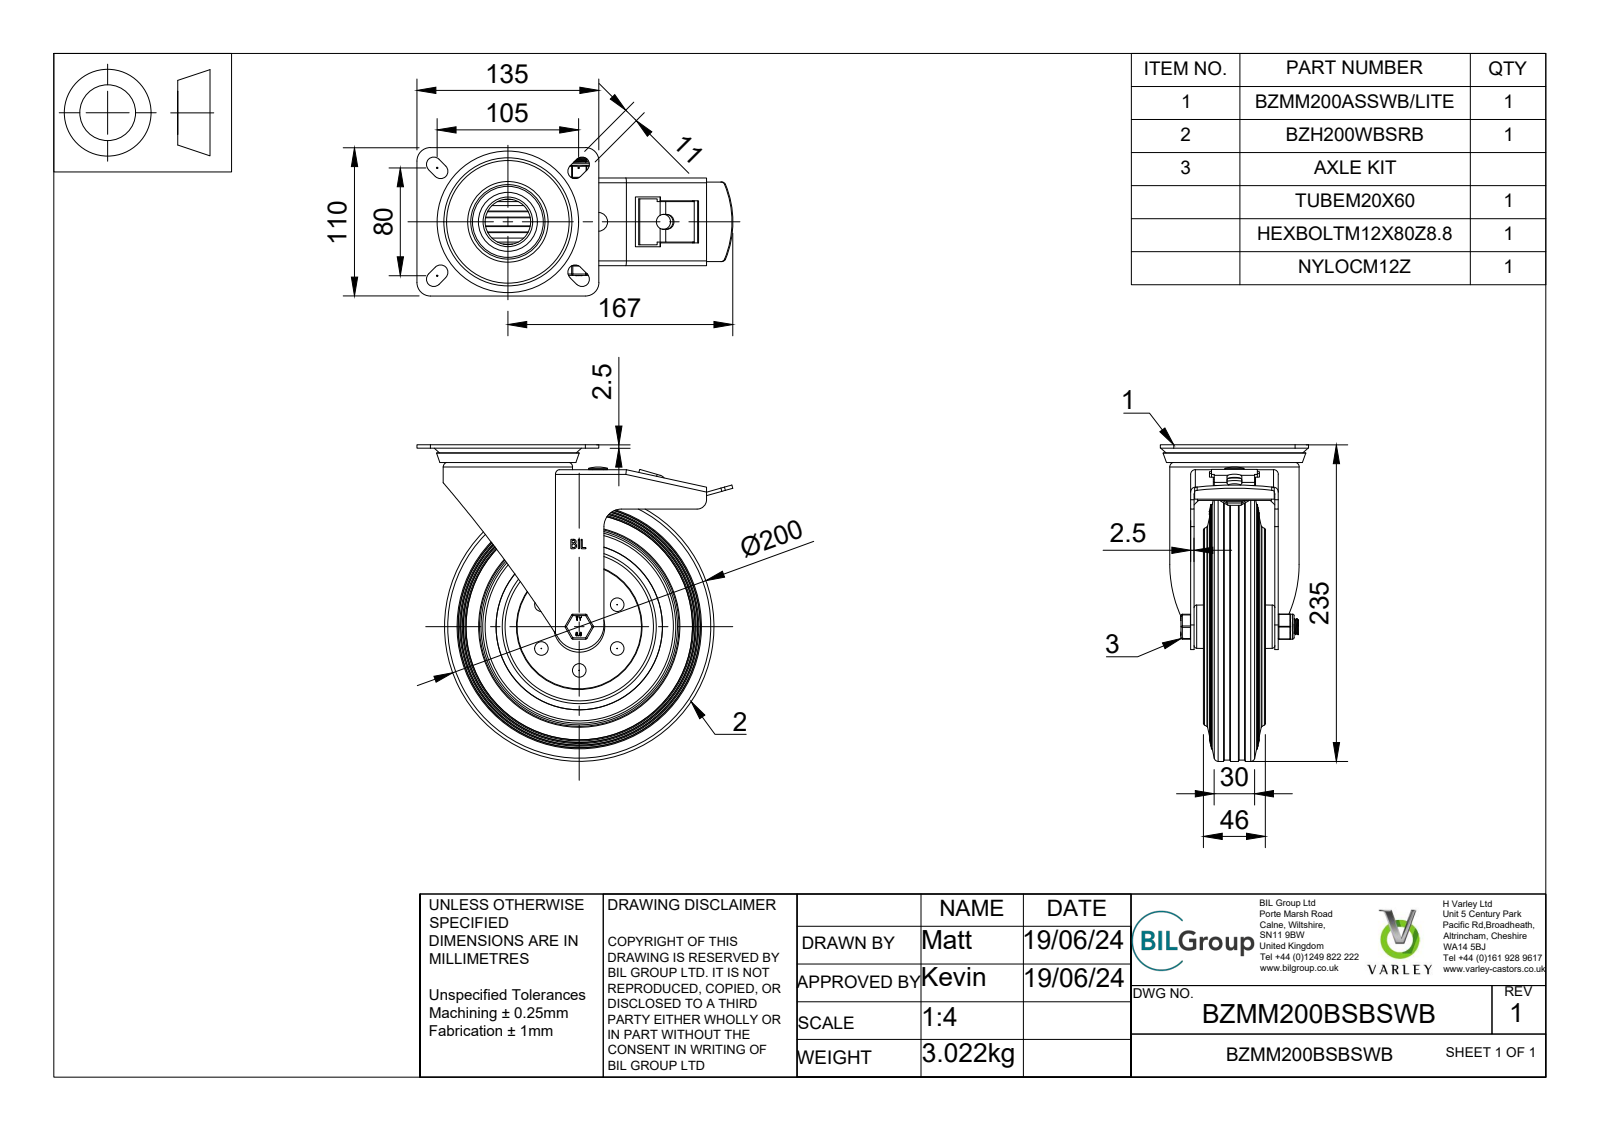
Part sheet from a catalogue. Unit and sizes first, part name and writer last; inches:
Units: inches
Overall size (bounding box): 9.252 × 9.232 × 4.331
Round holes (diameter × count): ⌀0.197 ×6, ⌀0.315 ×1, ⌀0.433 ×1, ⌀0.472 ×1, ⌀0.48 ×1, ⌀0.492 ×1, ⌀0.551 ×1, ⌀0.795 ×1, ⌀0.827 ×1, ⌀1.181 ×1, ⌀1.329 ×1, ⌀2.402 ×1
Round bosses / shafts (diameter × count): ⌀0.197 ×10, ⌀7.874 ×1, ⌀7.795 ×1, ⌀3.78 ×1, ⌀3.071 ×1, ⌀1.969 ×1, ⌀1.565 ×1, ⌀1.102 ×1
Partial cylindrical surfaces — rounded edges, fillets, slot ends (radius × count): R0.02 ×18, R0.039 ×12, R0.217 ×10, R0.069 ×7, R0.01 ×6, R0.098 ×6, R0.138 ×4, R0.394 ×4
Main face-to-face distances: 0.098, 2.461, 0.354, 0.079, 0.157, 1.24, 1.319, 1.142, 1.22, 0.512
Hole centre spacings: 1.28, 2.216, 2.217, 2.559, 2.559, 2.638
Volume: 67.92 in³ · Surface area: 493.2 in²
Bodies: 71 solids, 814 faces (356 planar, 210 cylindrical, 248 other)
Part name (STEP PRODUCT): BZMM200BSBSWB v5; BZMM200ASSWBLITE v1; ZINC PLATED, PRESSED STEEL TOP PLATE; ZINC PLATED, PRESSED STEEL TOP PLATE Geometry (+7 more)
STEP written by: Autodesk Translation Framework v13.14.0.145 (AUTOMOTIVE_DESIGN)
